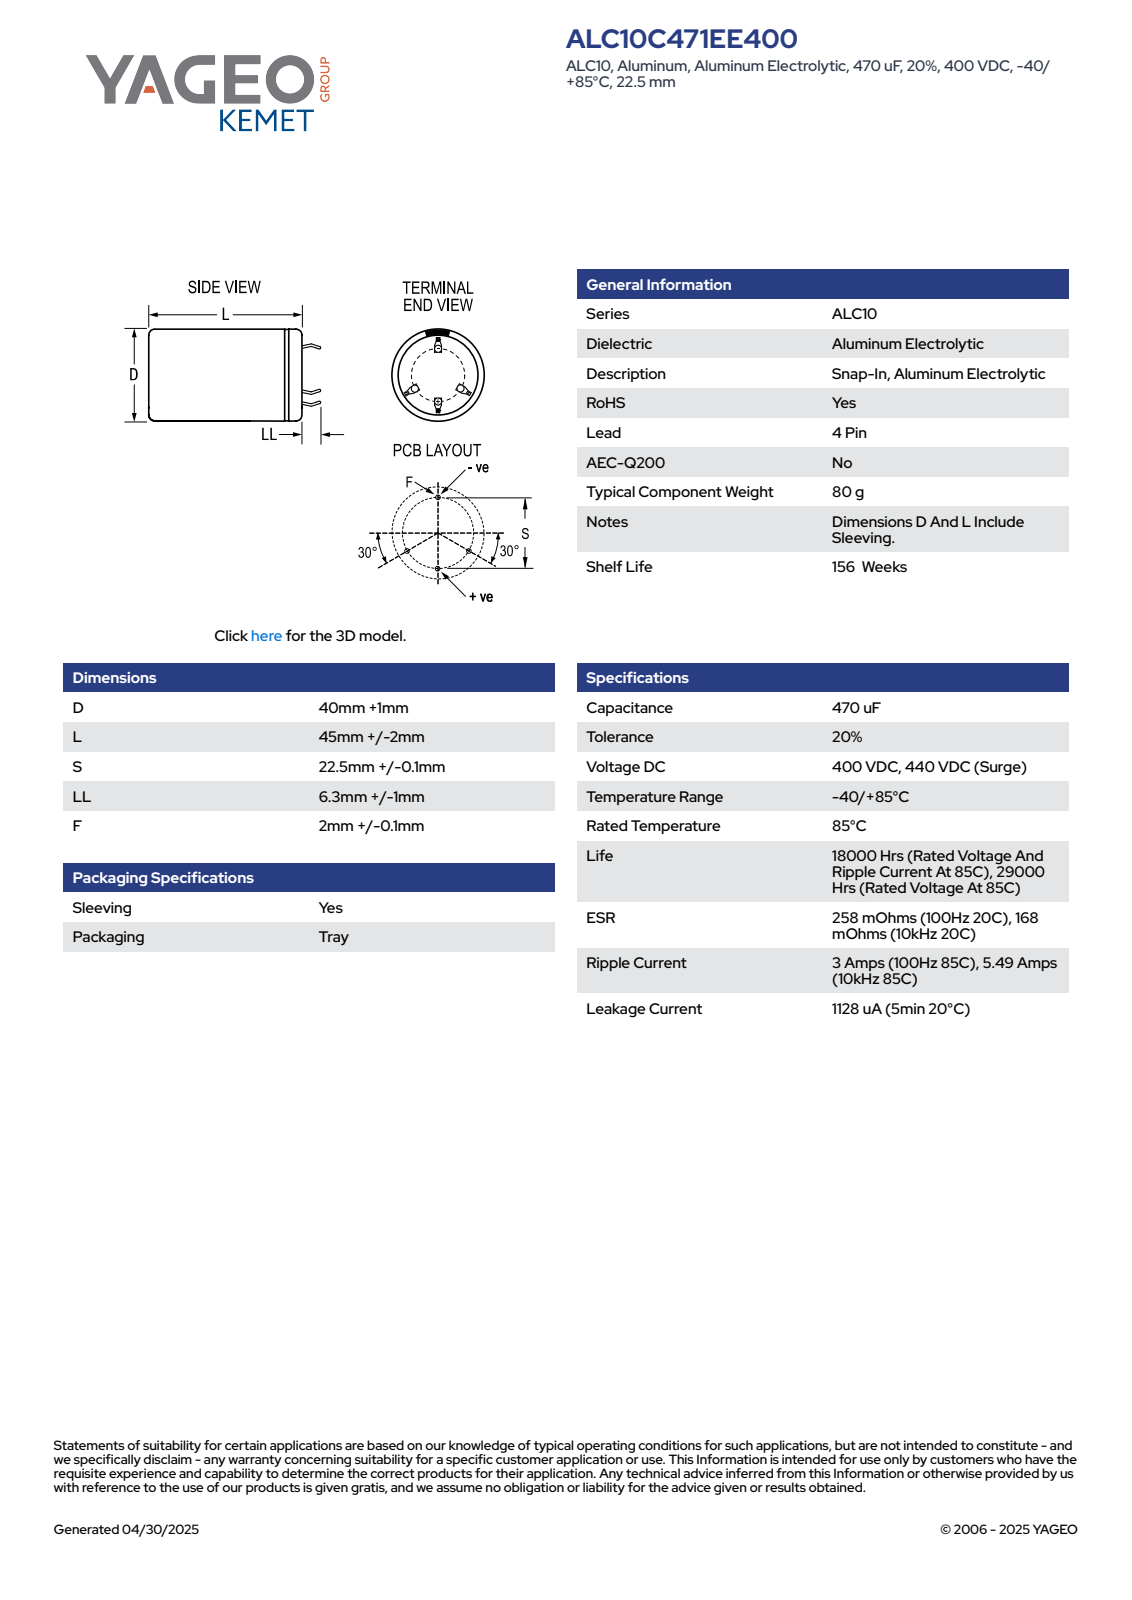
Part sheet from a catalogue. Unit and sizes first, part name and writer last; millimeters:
Units: millimetres
Overall size (bounding box): 54.29 × 41 × 41
Round holes (diameter × count): ⌀36.28 ×1
Round bosses / shafts (diameter × count): ⌀41 ×1
Partial cylindrical surfaces — rounded edges, fillets, slot ends (radius × count): R20.49 ×1
Main face-to-face distances: 46.99, 47.49, 0.5, 0.6, 0.4, 0.39, 0.75, 1.35, 19.93, 19.53
Volume: 61 280 mm³ · Surface area: 8 739 mm²
Bodies: 1 solid, 134 faces (80 planar, 15 cylindrical, 39 other)
Part name (STEP PRODUCT): CARS_K4P_40X45_D41L47S22.5LL7.3F2.1
STEP written by: SolidWorks 2014 (AUTOMOTIVE_DESIGN)
